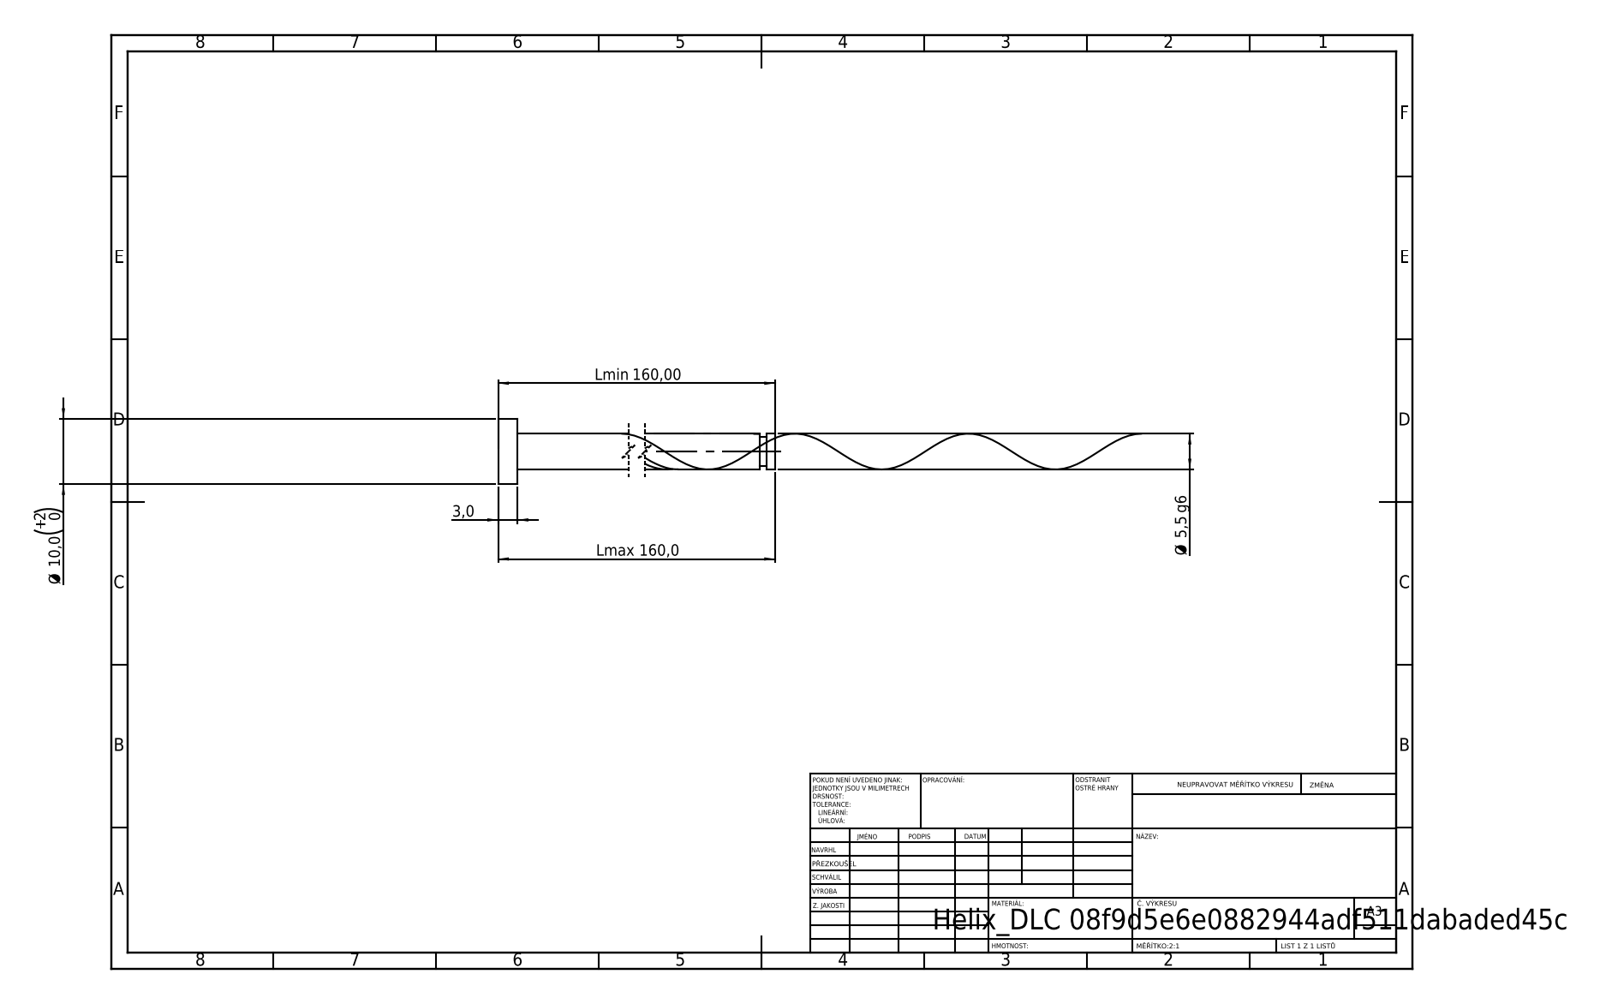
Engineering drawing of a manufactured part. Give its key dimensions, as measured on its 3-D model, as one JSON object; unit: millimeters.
{"step_written_by": "SolidWorks 2019 (CONFIG_CONTROL_DESIGN)", "units": "millimeters", "bodies": {"solids": 1, "faces": 21, "planar": 6, "cylindrical": 14, "other": 1}, "overall_size": [160, 10, 10], "volume_mm3": 3920, "surface_area_mm2": 3031, "round_bosses_or_shafts": [[10, 1], [5.5, 1], [4.4, 1]], "face_to_face_distances": [3, 160, 157, 158.76, 155.76, 1.24, 157.66, 154.66, 1.1, 2.34]}
